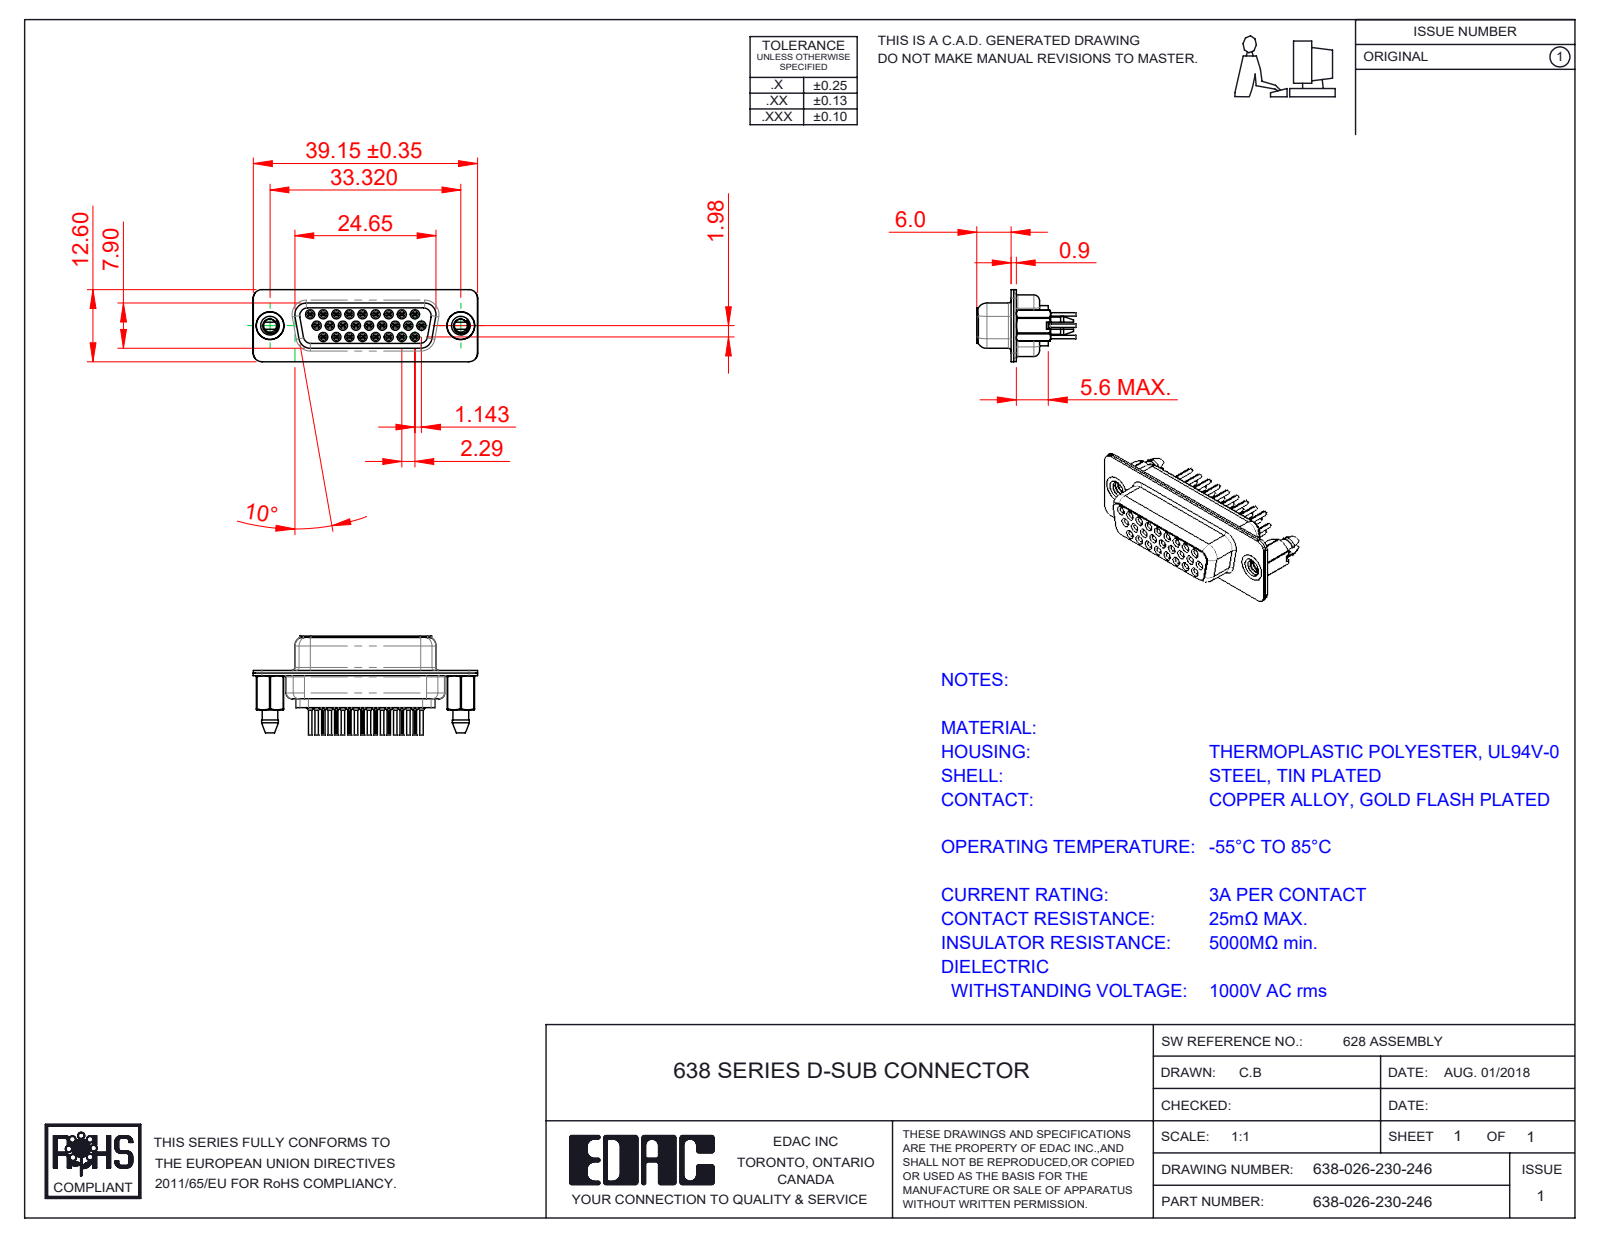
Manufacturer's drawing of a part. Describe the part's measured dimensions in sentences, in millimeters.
The part is named "638 Shell Front_26 Contacts; 638-026-230-246; 638 Housing_26 Contacts; 638 Shell Rear_26 Contacts (+4 more)". Its 3-D file was written by "SolidWorks 2020 (CONFIG_CONTROL_DESIGN)". It is 31 solids with 3655 faces: 905 planar, 1027 cylindrical and 1723 other. Overall it measures 39.19 by 17.3 by 12.6 millimeters. Its volume is 2 326 cubic millimeters and its surface area 8 592 square millimeters. Round holes: 26 of diameter 0.2, 26 of diameter 0.8, 26 of diameter 1, 26 of diameter 1.1, 26 of diameter 1.6, 26 of diameter 1.7, 26 of diameter 1.8, 2 of diameter 2.26, 2 of diameter 4, 2 of diameter 4.05, 2 of diameter 4.85. Round bosses or shafts: 26 of diameter 2, 26 of diameter 1.5, 26 of diameter 1.2, 26 of diameter 0.6, 2 of diameter 4.95, 2 of diameter 4.8. Partial cylindrical surfaces (rounded edges, fillets, slot ends): 52 of radius 0.1, 22 of radius 1.5, 18 of radius 0.28, 12 of radius 2, 8 of radius 1.55, 5 of radius 1.35, 4 of radius 0.25, 4 of radius 0.5. The main face-to-face distances are 0.45, 0.4, 1.43, 8.88, 6.6, 0.9, 2.28, 1.4, 0.85, 7.05. The hole center spacings are 3.96, 2.28, 4.57, 6.05, 2.29, 8.24, 6.86, 10.48.
